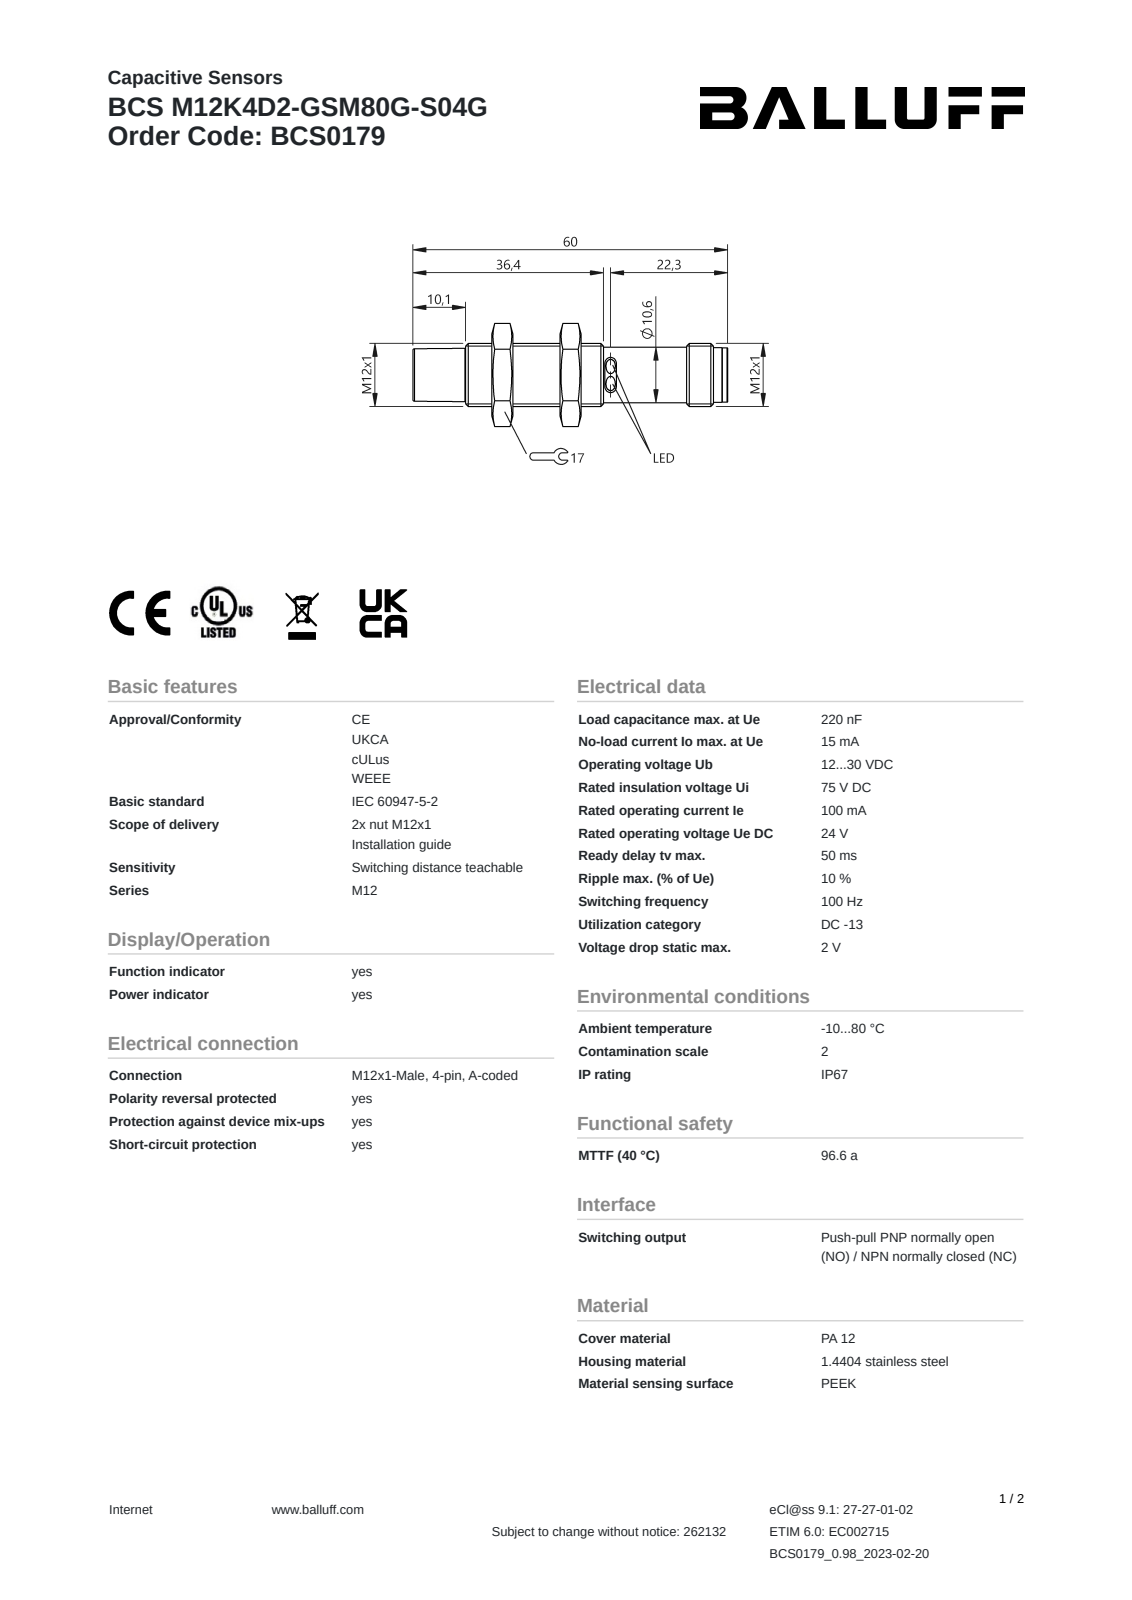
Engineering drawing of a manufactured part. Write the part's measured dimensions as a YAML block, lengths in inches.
part_name: "BCS0179"
step_written_by: "SolidWorks 2021 (AUTOMOTIVE_DESIGN)"
units: inches
bodies: {solids: 3, faces: 111, planar: 38, cylindrical: 30, other: 43}
overall_size: [2.362, 0.773, 0.669]
volume: 0.407
surface_area: 6.149
round_holes:
  - {diameter: 0.331, count: 1}
  - {diameter: 0.43, count: 1}
round_bosses_or_shafts:
  - {diameter: 0.039, count: 4}
  - {diameter: 0.472, count: 1}
  - {diameter: 0.417, count: 1}
  - {diameter: 0.407, count: 1}
  - {diameter: 0.386, count: 1}
partial_cylinders:
  - {radius: 0.028, count: 4}
  - {radius: 0.075, count: 4}
  - {radius: 0.012, count: 2}
  - {radius: 0.043, count: 2}
  - {radius: 0.024, count: 1}
  - {radius: 0.18, count: 1}
  - {radius: 0.182, count: 1}
face_to_face_distances: [0.516, 0.157, 0.669, 0.673, 0.358, 1.264, 1.106, 0.748, 0.591, 0.752]
